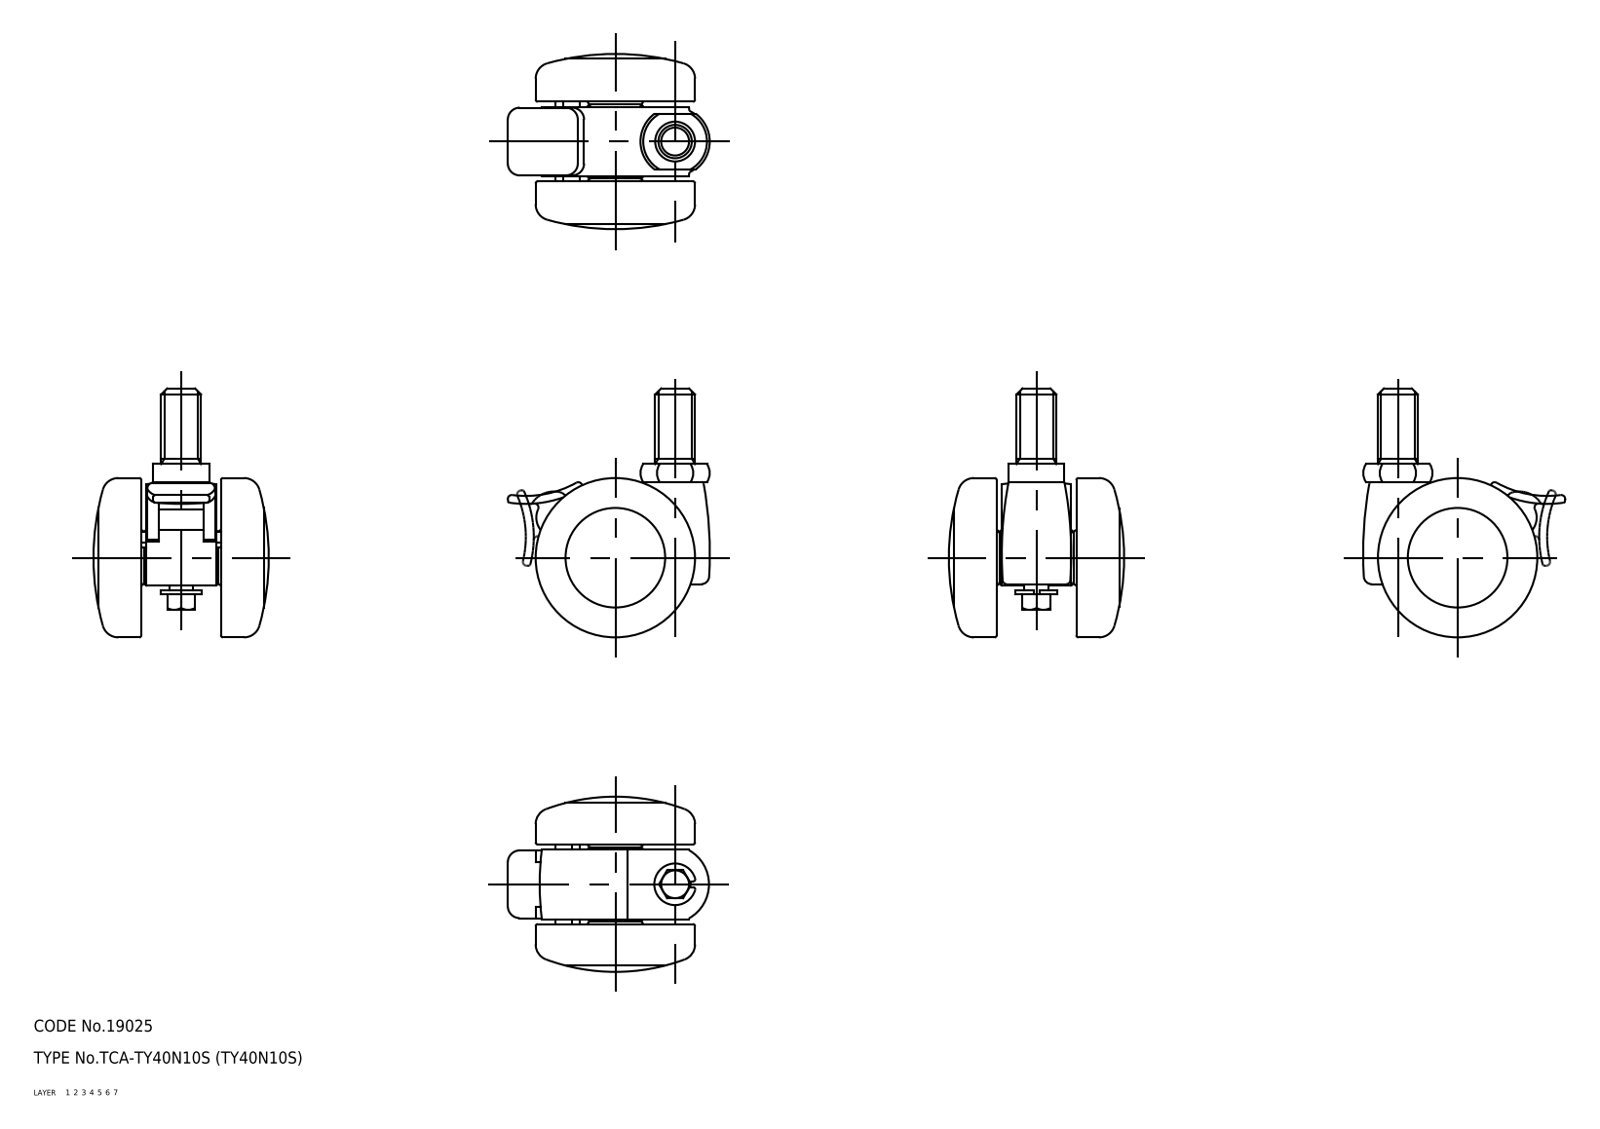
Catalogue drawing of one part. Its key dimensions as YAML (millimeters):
part_name: "wheel; main shaft; lever; TY40N10S_10221_36"
step_written_by: "CADfix (AUTOMOTIVE_DESIGN)"
units: millimeters
bodies: {solids: 5, faces: 193, planar: 0, cylindrical: 0, other: 193}
overall_size: [62.5, 50.72, 44]
volume: 40387
surface_area: 19322
